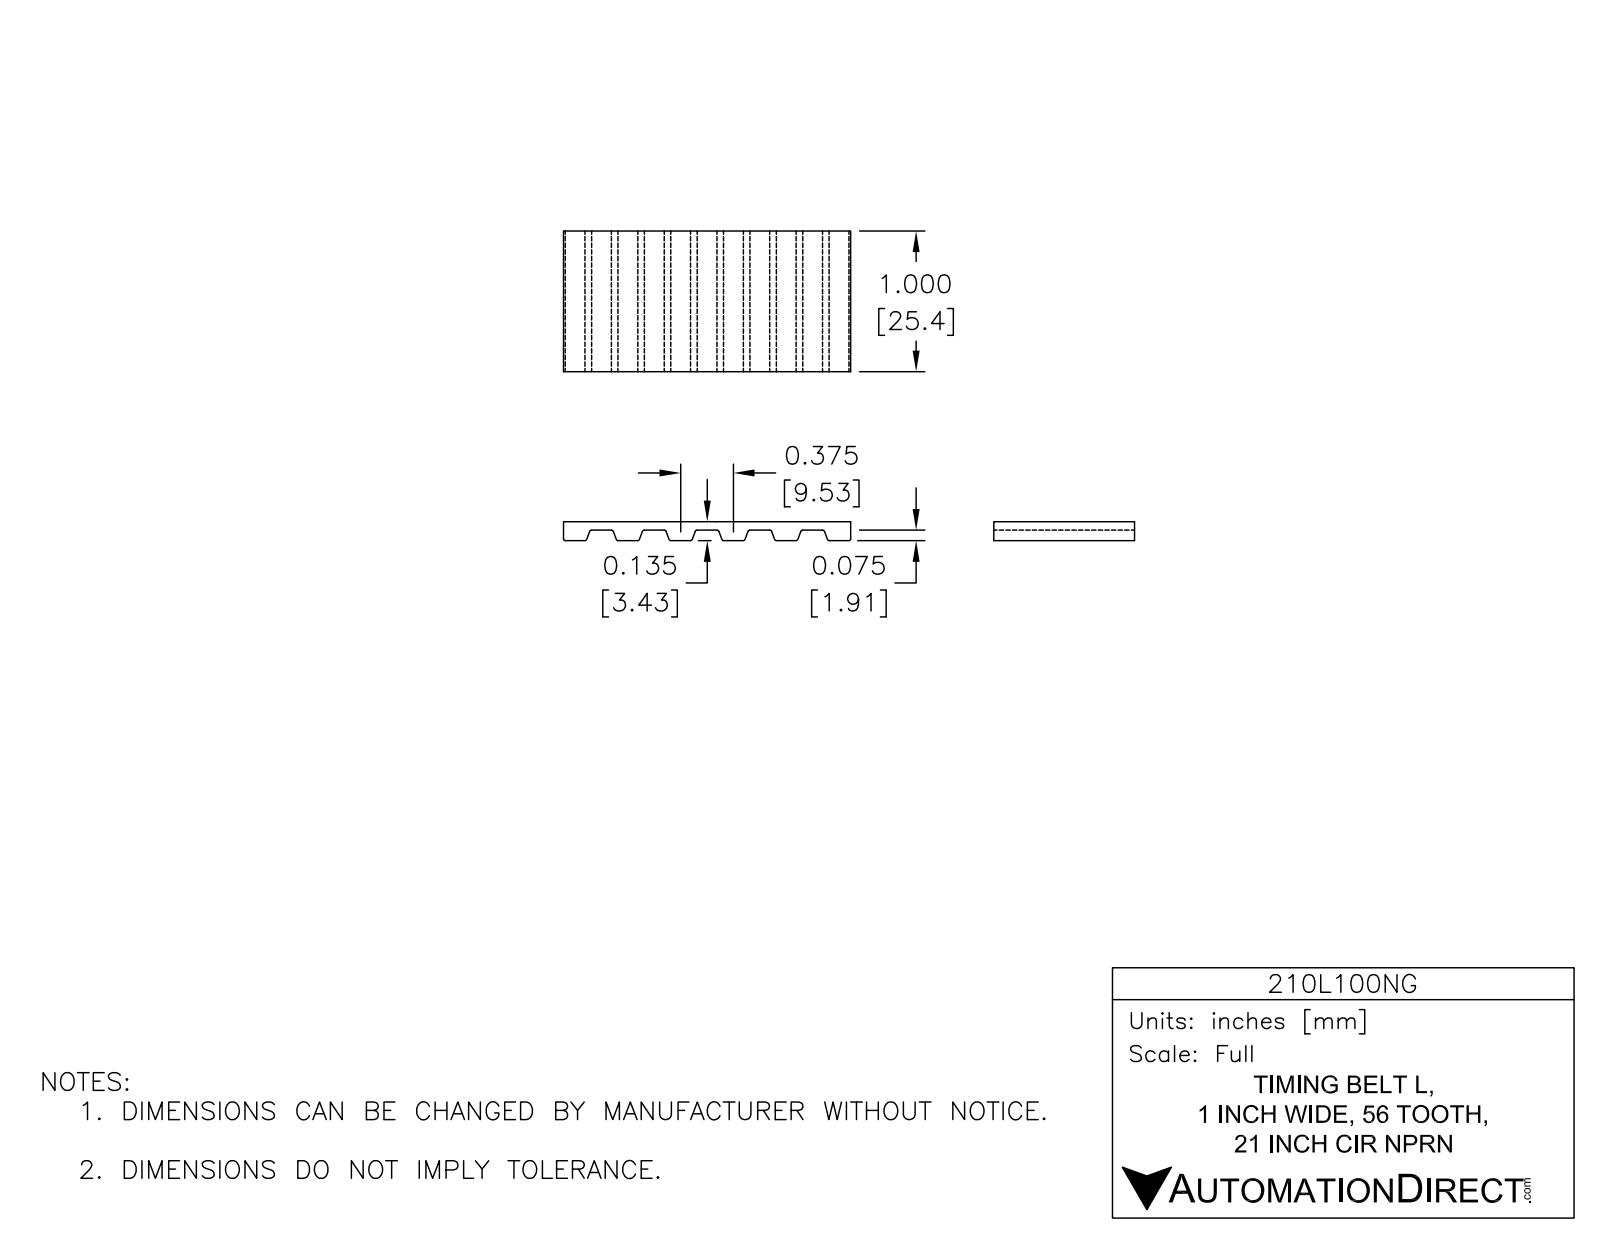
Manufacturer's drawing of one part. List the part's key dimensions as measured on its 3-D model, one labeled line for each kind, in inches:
Part name (STEP PRODUCT): 210L100NG
STEP written by: SolidWorks 2014 (AUTOMOTIVE_DESIGN)
Units: inches
Bodies: 1 solid, 462 faces (200 planar, 262 cylindrical, 0 other)
Overall size (bounding box): 8.788 × 3 × 1
Volume: 1.89 in³ · Surface area: 50.34 in²
Partial cylindrical surfaces — rounded edges, fillets, slot ends (radius × count): R0.02 ×220, R1.435 ×2, R1.5 ×2
Main face-to-face distances: 0.065, 2.935, 3, 2.87, 0.14, 2.86, 0.075, 2.795, 1, 2.72
